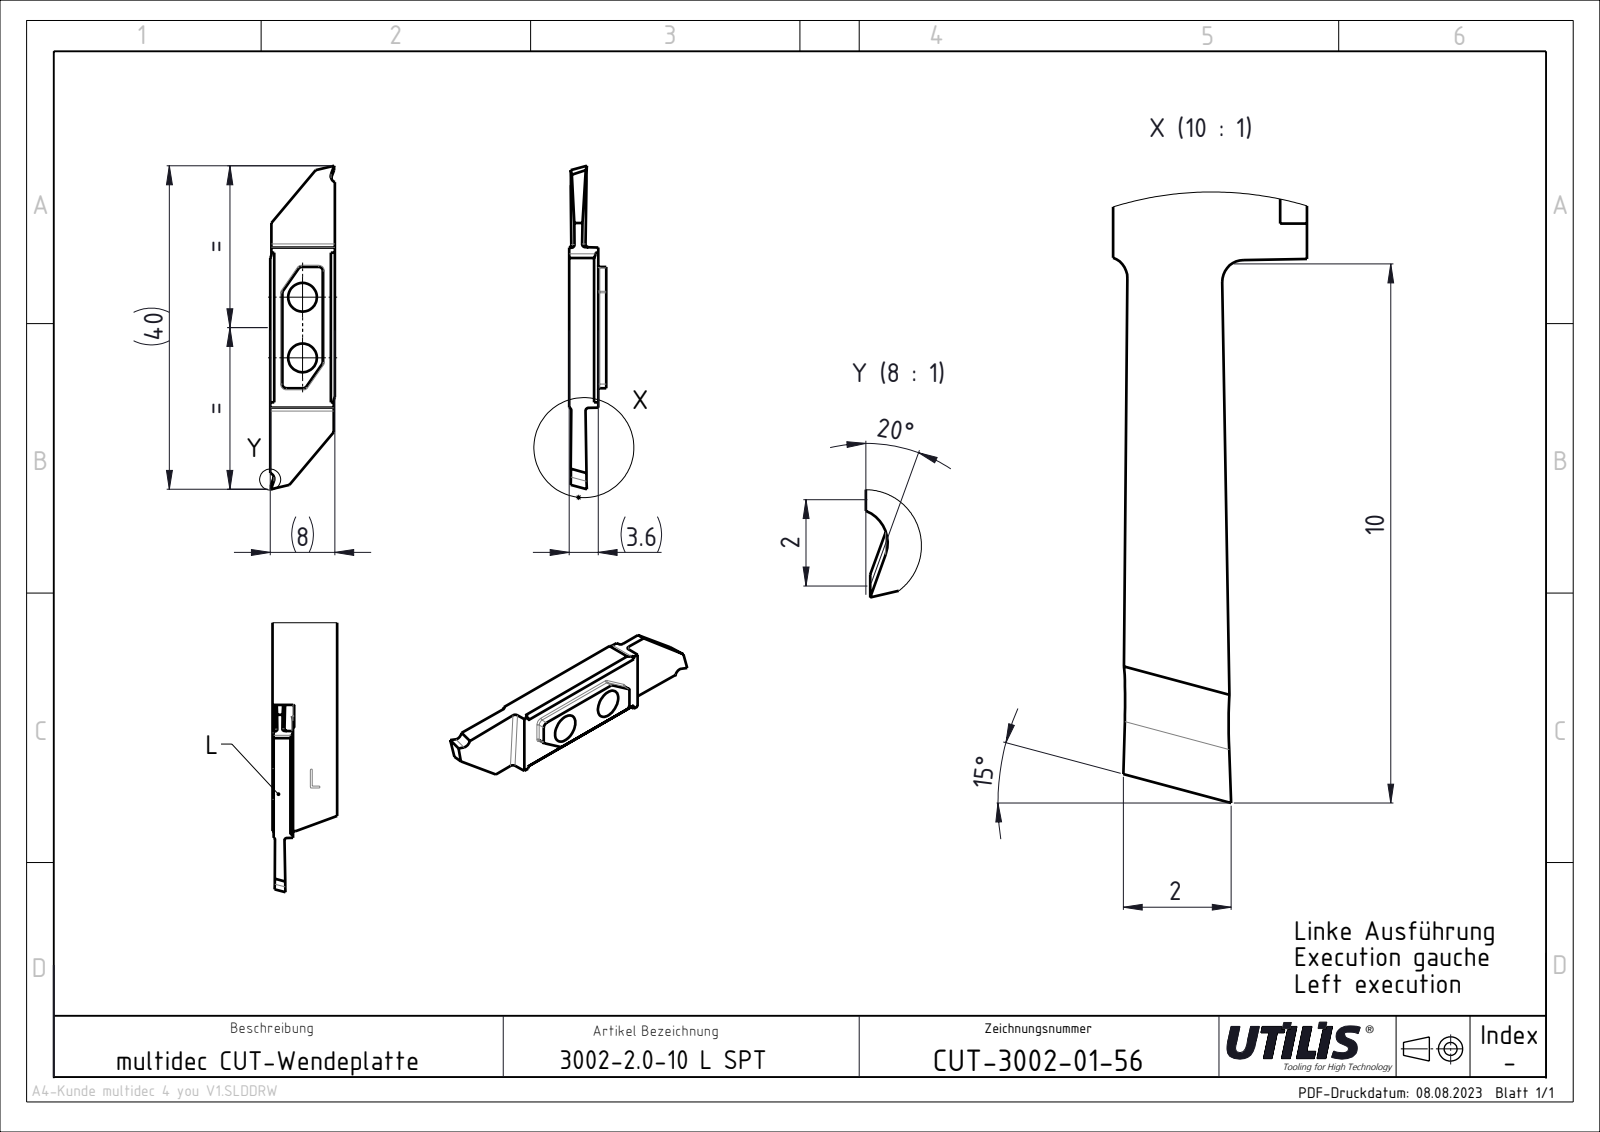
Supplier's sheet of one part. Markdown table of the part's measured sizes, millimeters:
| quantity | value |
| --- | --- |
| part name | CUT-3002 SPT; ASME Y14.5 |
| STEP written by | SolidWorks 2023 SP4 \|\| FormatWorks Professional (AP242_MANAGED_MODEL_BASED_3D_ENGINEERING_MIM_LF) |
| units | millimeters |
| bodies | 1 solid, 32 faces (22 planar, 10 cylindrical, 0 other) |
| overall size | 40 × 8 × 3.6 |
| volume | 708 mm³ |
| surface area | 835 mm² |
| round holes (diameter × count) | 3.55 × 2 |
| partial cylindrical surfaces (radius × count) | 0.4 × 4, 1 × 2 |
| main face-to-face distances | 3.6, 8, 22.54, 7.85, 7.7, 18.5 |
| hole center spacings | 7.49 |
